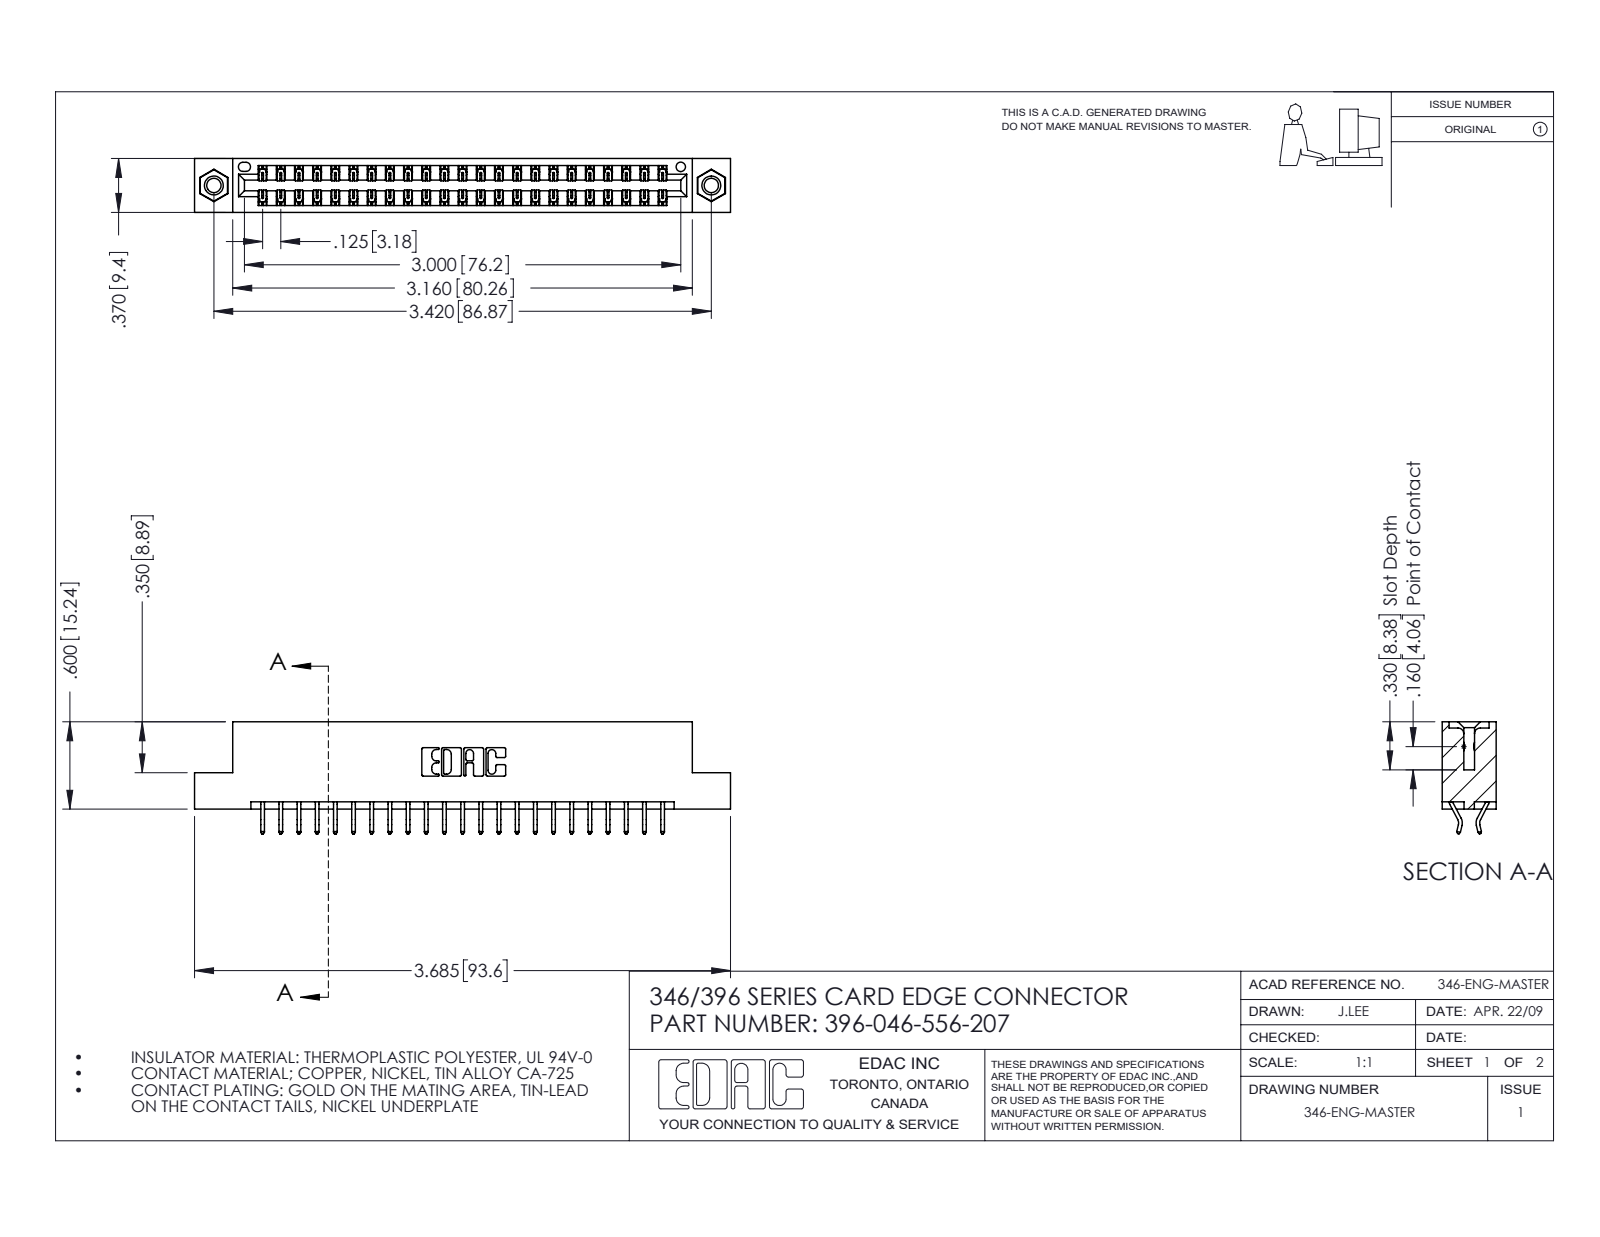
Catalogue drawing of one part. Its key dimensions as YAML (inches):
part_name: "346 Part_Flush Mounting Lugs - 0.156 Dia-TI; 396-046-556-207; 345-250-001_345-250-005-103; 345-292-001_556 Tail"
step_written_by: "SolidWorks 2016 (CONFIG_CONTROL_DESIGN)"
units: inches
bodies: {solids: 49, faces: 2850, planar: 1902, cylindrical: 932, other: 16}
overall_size: [3.685, 0.77, 0.37]
volume: 0.547
surface_area: 18.62
round_holes:
  - {diameter: 0.098, count: 2}
  - {diameter: 0.125, count: 2}
  - {diameter: 0.156, count: 2}
  - {diameter: 0.064, count: 1}
round_bosses_or_shafts:
  - {diameter: 0.155, count: 2}
partial_cylinders:
  - {radius: 0.006, count: 69}
  - {radius: 0.01, count: 22}
  - {radius: 0.007, count: 6}
  - {radius: 0.031, count: 6}
  - {radius: 0.026, count: 3}
  - {radius: 0.01, count: 2}
  - {radius: 0.014, count: 2}
  - {radius: 0.022, count: 2}
face_to_face_distances: [0.048, 0.322, 0.25, 0.37, 0.025, 0.072, 0.298, 0.275, 0.148, 0.222]
hole_center_spacings: [0.246, 3.212, 3.42]
